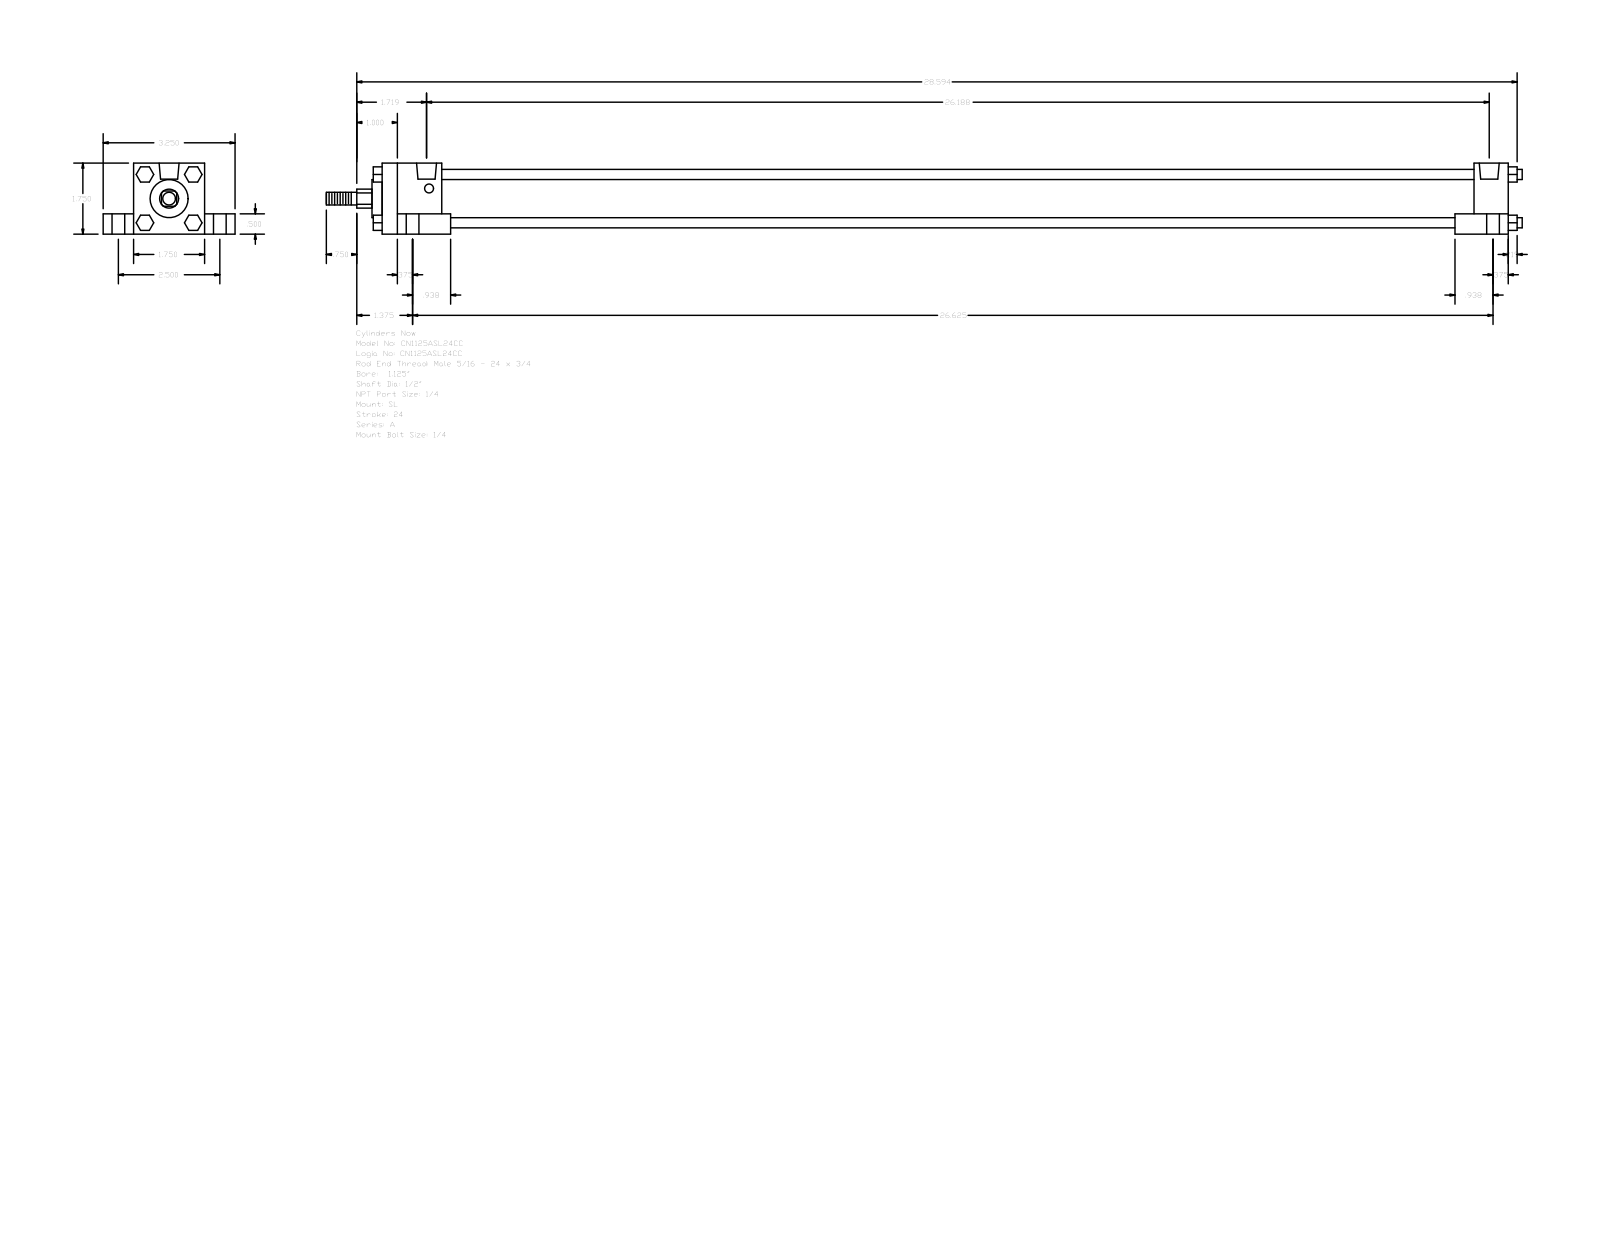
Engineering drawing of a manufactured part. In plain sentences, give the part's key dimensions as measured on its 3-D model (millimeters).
The part is named "A_SL__0112_0.5". Its 3-D file was written by "GSSL Pune (CONFIG_CONTROL_DESIGN)". It is 0 solids with 150 faces: 114 planar, 36 cylindrical and 0 other. Overall it measures 748.51 by 82.55 by 44.45 millimeters. Round holes: 4 of diameter 5.56, 4 of diameter 7.94, 4 of diameter 14.29, 2 of diameter 12.49. Round bosses or shafts: 4 of diameter 6.35, 1 of diameter 31.88, 1 of diameter 23.81, 1 of diameter 12.7, 1 of diameter 7.94. Partial cylindrical surfaces (rounded edges, fillets, slot ends): 1 of radius 5.94. The main face-to-face distances are 44.46, 31.76, 12.7, 19.04, 63.5, 704.85, 683.41, 21.44, 37.3, 646.11. The hole center spacings are 31.84, 32, 32.93, 33.39, 63.5, 661.99, 666.72, 668.29.
